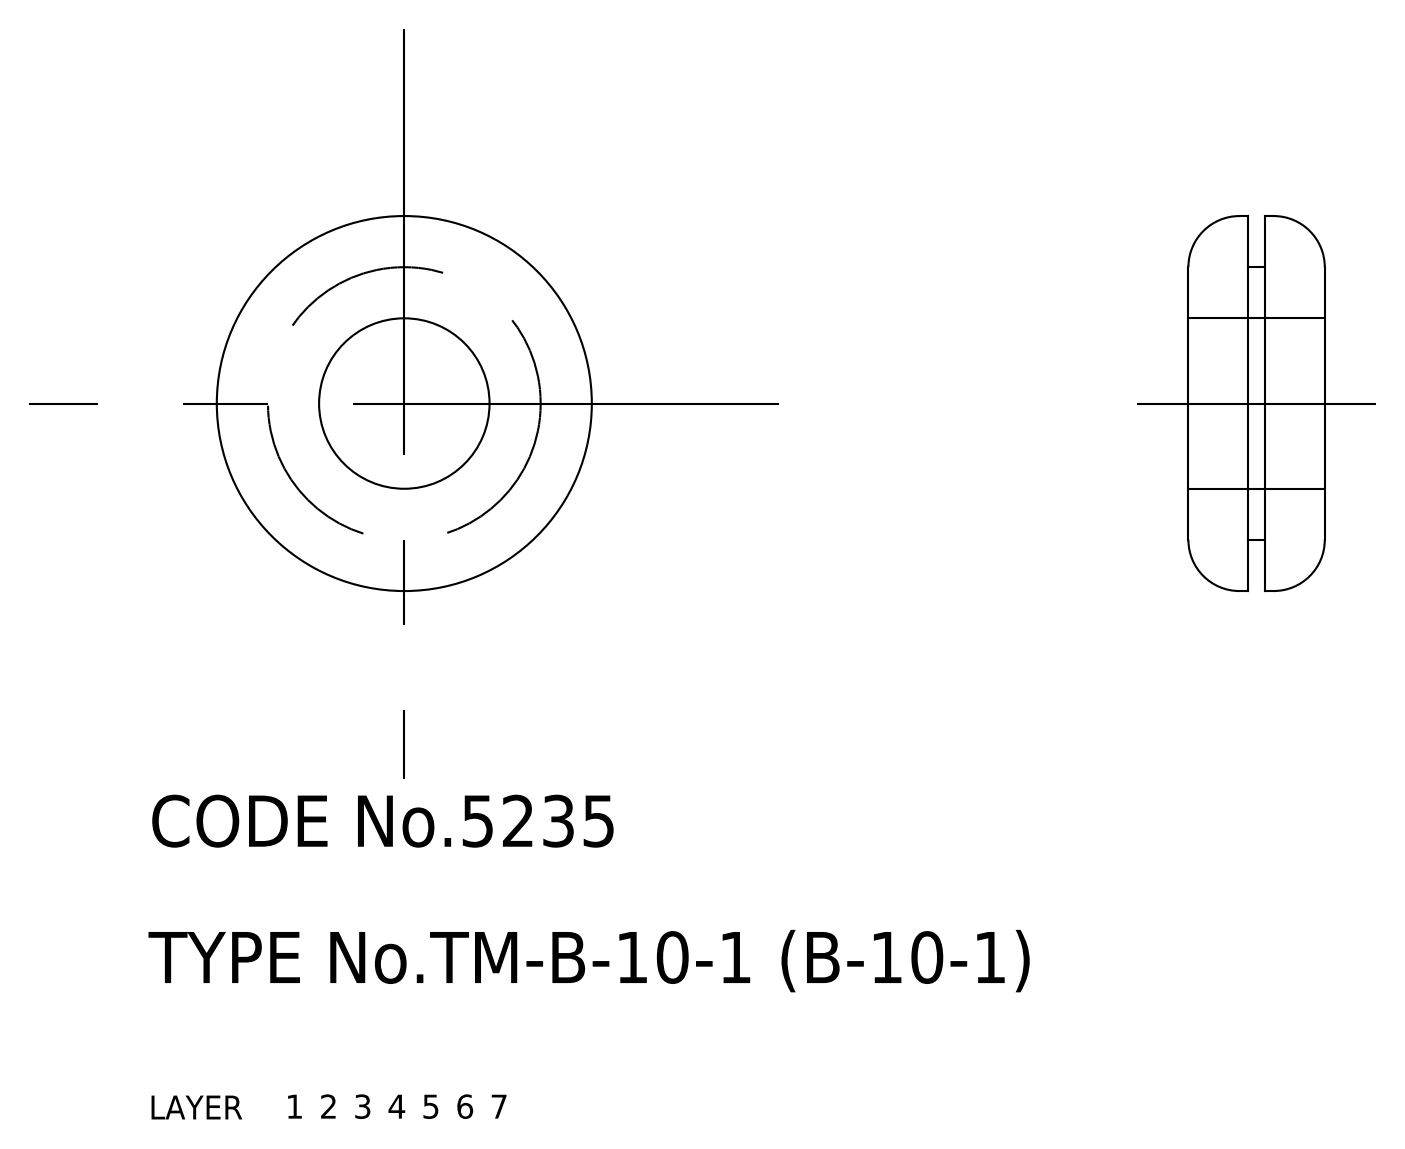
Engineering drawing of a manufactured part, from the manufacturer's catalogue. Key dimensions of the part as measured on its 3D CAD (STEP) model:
Part name (STEP PRODUCT): grommet
STEP written by: CADfix (AUTOMOTIVE_DESIGN)
Units: millimetres
Bodies: 1 solid, 16 faces (0 planar, 0 cylindrical, 16 other)
Overall size (bounding box): 22 × 22 × 8
Volume: 1 988 mm³ · Surface area: 1 561 mm²
